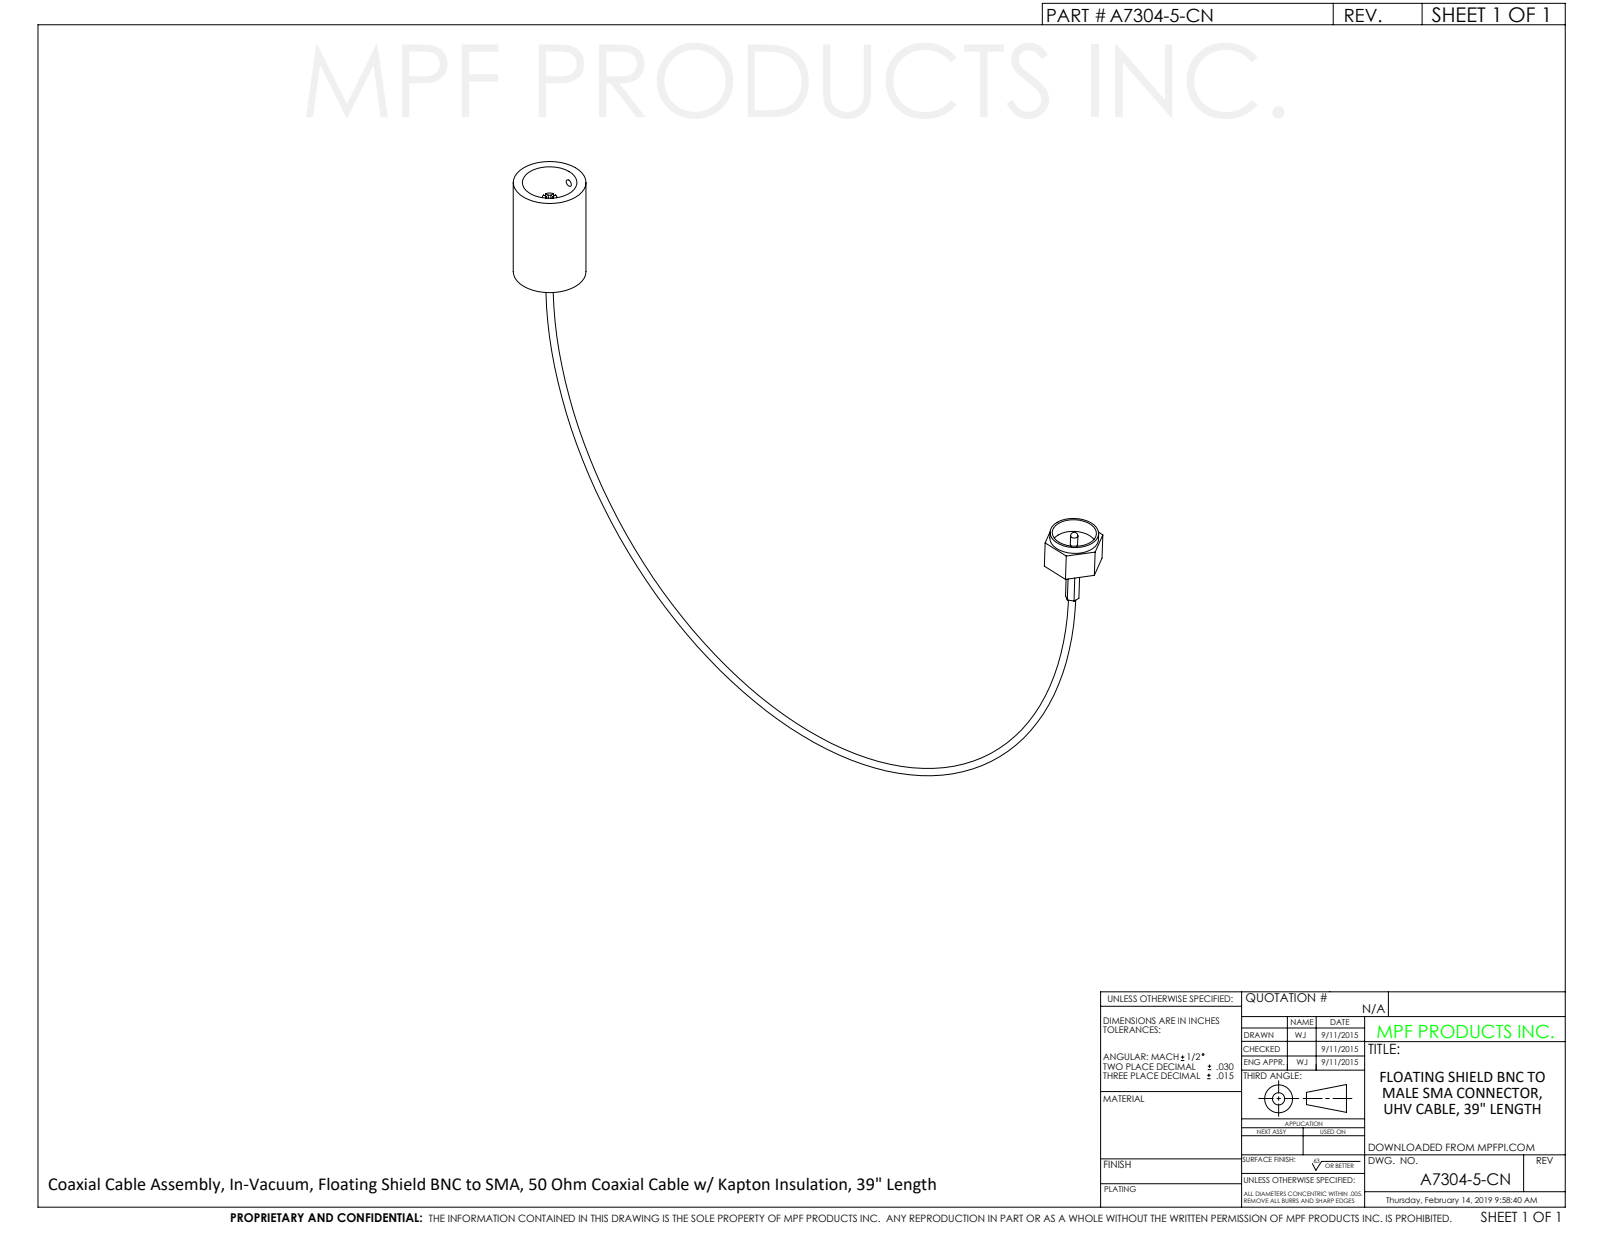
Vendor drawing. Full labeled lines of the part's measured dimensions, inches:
Part name (STEP PRODUCT): A7304-5-CN
STEP written by: SolidWorks 2012 (CONFIG_CONTROL_DESIGN)
Units: inches
Bodies: 1 solid, 71 faces (38 planar, 26 cylindrical, 7 other)
Overall size (bounding box): 11.11 × 6.833 × 1
Volume: 1.16 in³ · Surface area: 16.55 in²
Round holes (diameter × count): ⌀0.1 ×3, ⌀0.2 ×1, ⌀0.609 ×1, ⌀0.75 ×1
Round bosses / shafts (diameter × count): ⌀1 ×1, ⌀0.669 ×1, ⌀0.2 ×1, ⌀0.1 ×1
Main face-to-face distances: 1.5, 0.712, 0.3, 0.712, 0.1, 0.165, 0.4, 0.5, 0.2, 0.165
Hole centre spacings: 0.35
